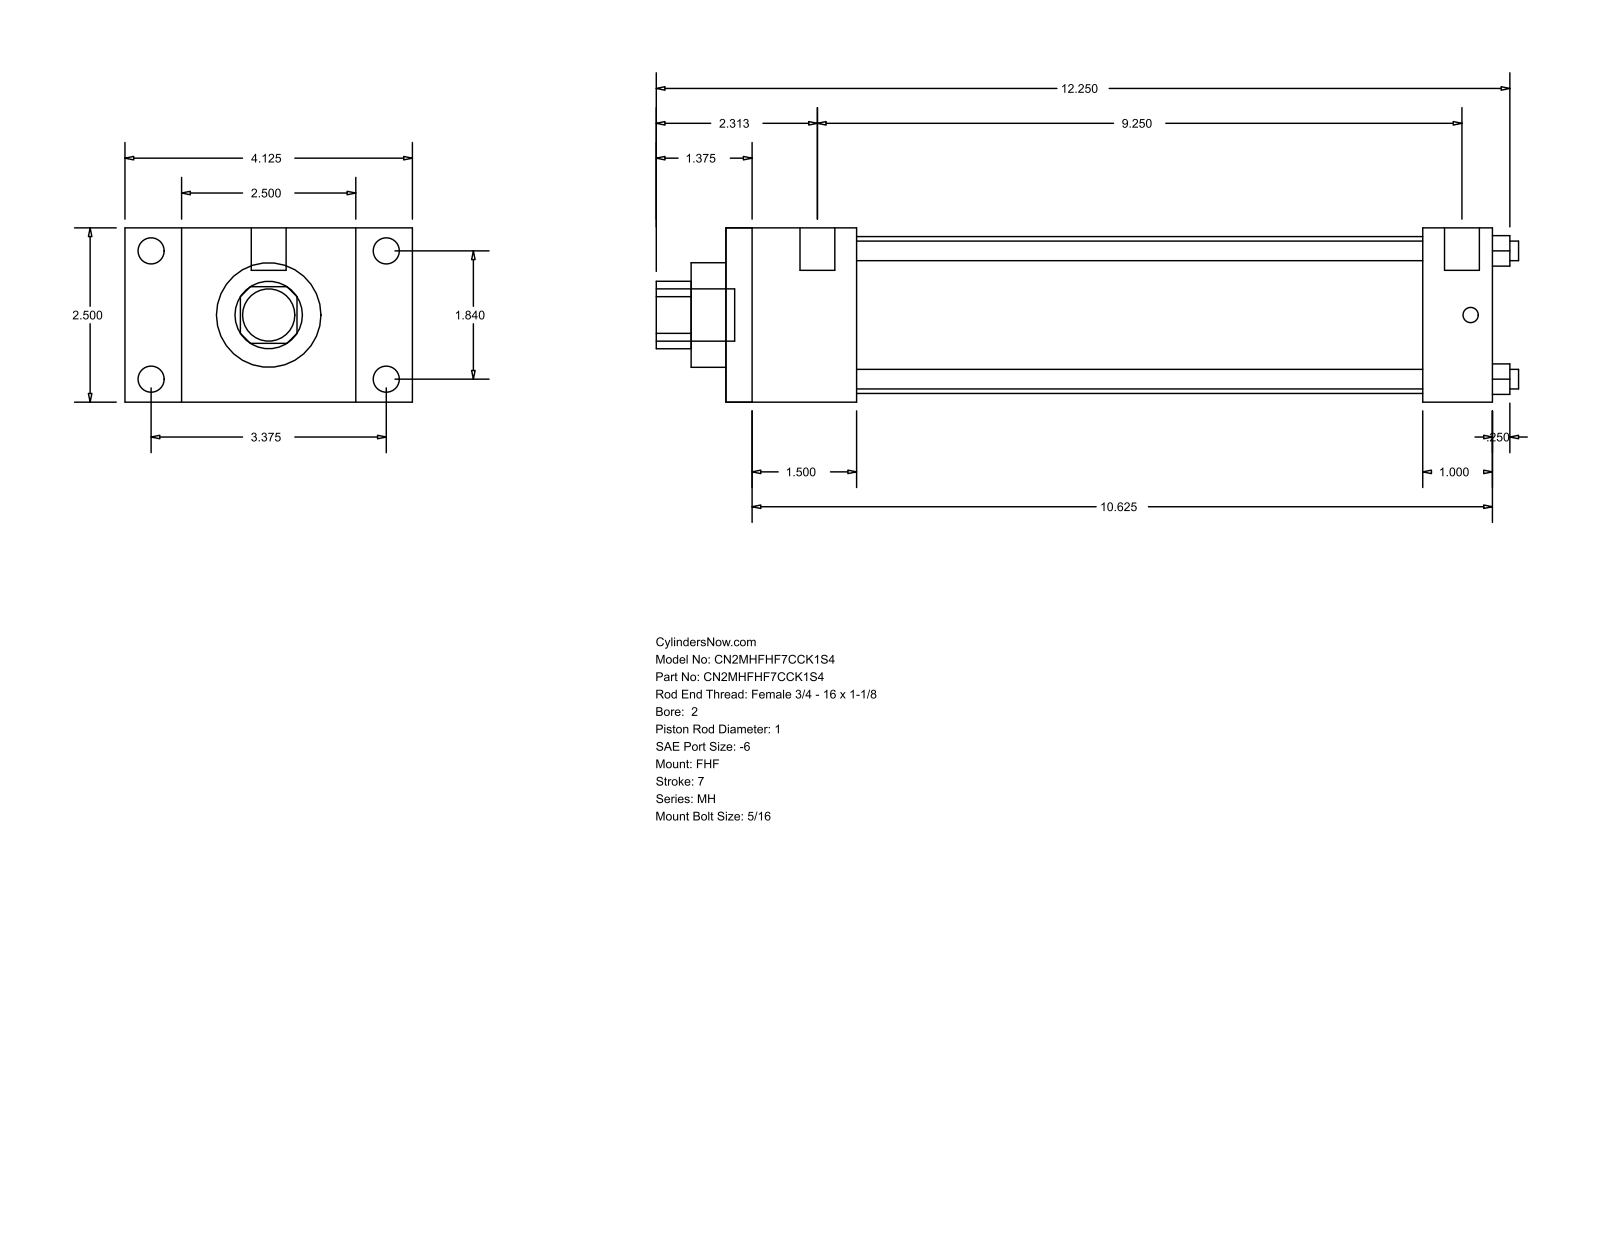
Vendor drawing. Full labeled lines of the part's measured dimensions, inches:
Part name (STEP PRODUCT): MH_FHF__0200_1
STEP written by: GSSL Pune (CONFIG_CONTROL_DESIGN)
Units: inches
Bodies: 0 solids, 88 faces (60 planar, 28 cylindrical, 0 other)
Overall size (bounding box): 12.375 × 4.125 × 2.5
Round holes (diameter × count): ⌀0.281 ×4, ⌀1 ×1, ⌀1.5 ×1, ⌀2.25 ×1
Round bosses / shafts (diameter × count): ⌀0.375 ×4, ⌀0.219 ×4, ⌀0.5 ×2, ⌀0.75 ×1
Partial cylindrical surfaces — rounded edges, fillets, slot ends (radius × count): R0.484 ×1
Main face-to-face distances: 2.5, 11, 1.875, 9.125, 0.813, 3.313, 4.125, 1, 10, 8.125
Hole centre spacings: 1.301, 1.84, 2.602
